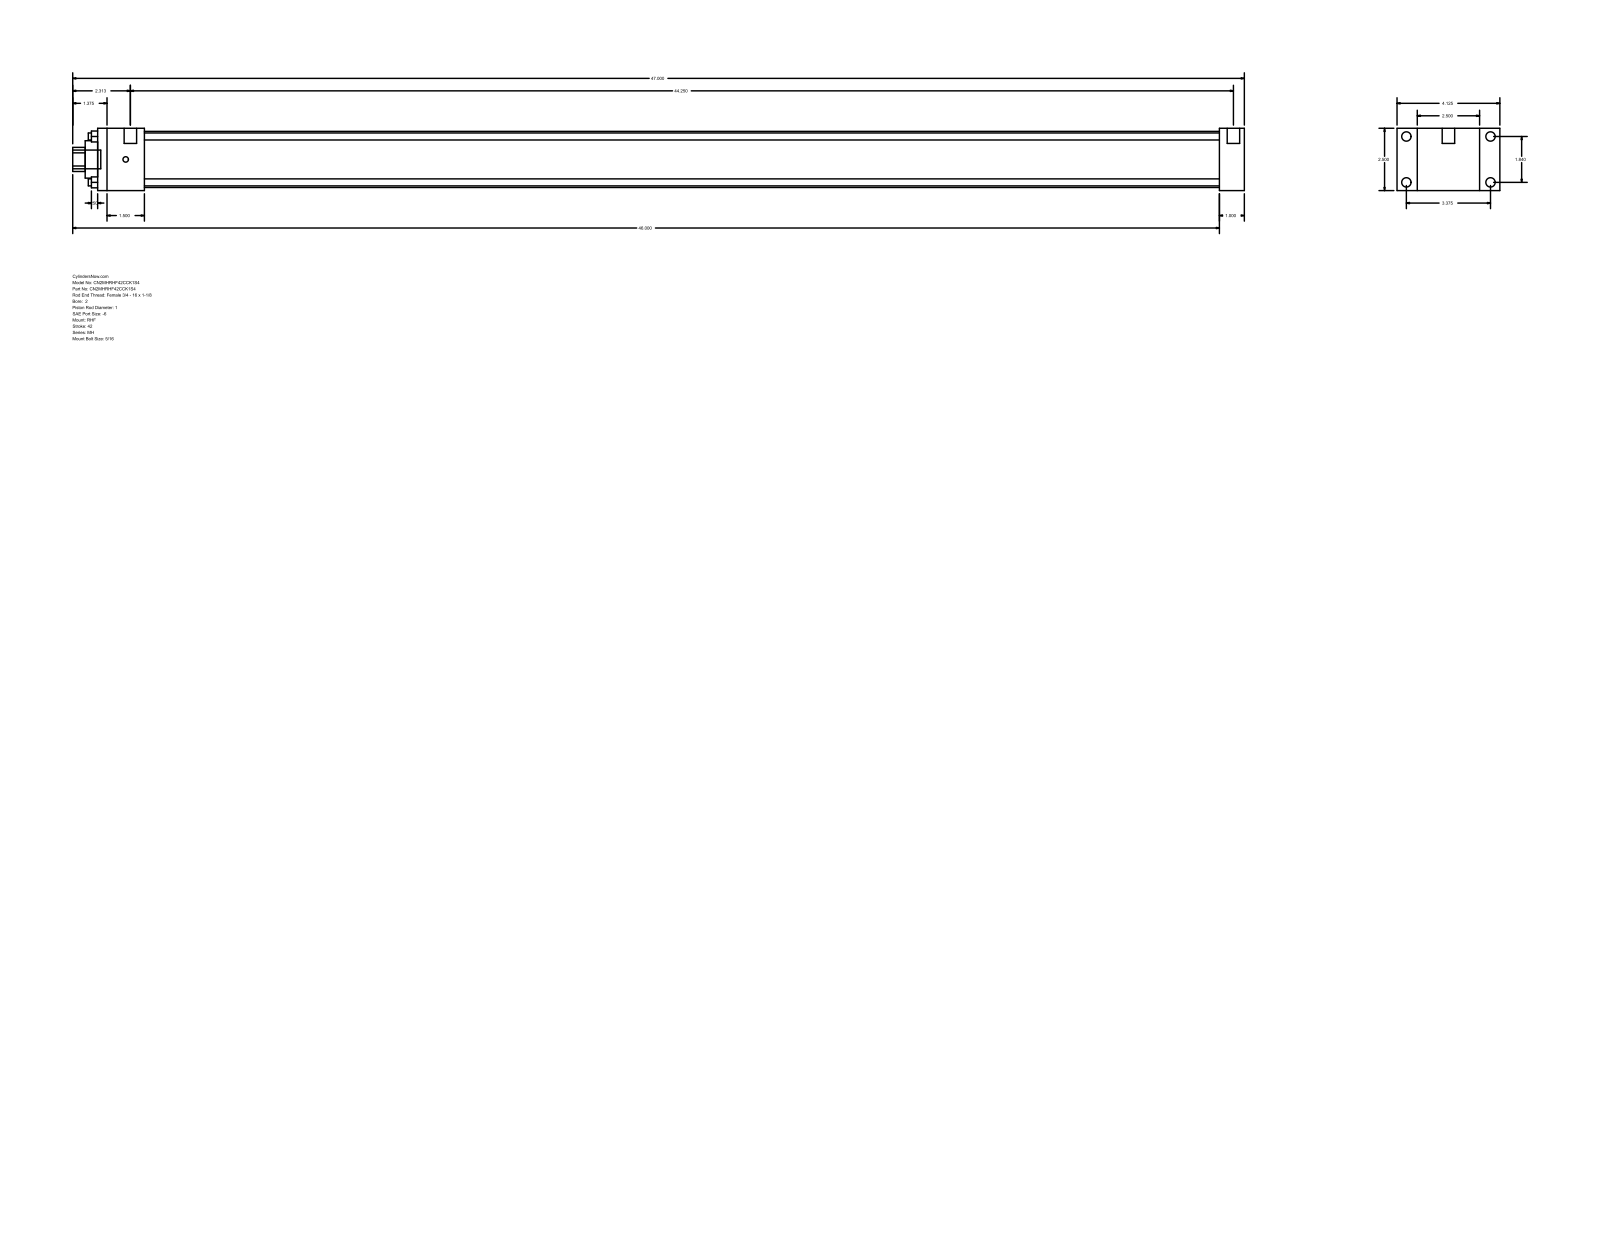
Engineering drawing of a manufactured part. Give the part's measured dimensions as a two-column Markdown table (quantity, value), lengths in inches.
| quantity | value |
| --- | --- |
| part name | MH_RHF__0200_1 |
| STEP written by | GSSL Pune (CONFIG_CONTROL_DESIGN) |
| units | inches |
| bodies | 0 solids, 88 faces (60 planar, 28 cylindrical, 0 other) |
| overall size | 47 × 4.125 × 2.5 |
| round holes (diameter × count) | 0.281 × 4, 1 × 1, 1.5 × 1, 2.25 × 1 |
| round bosses / shafts (diameter × count) | 0.375 × 4, 0.219 × 4, 0.5 × 2, 0.75 × 1 |
| partial cylindrical surfaces (radius × count) | 0.484 × 1 |
| main face-to-face distances | 2.5, 1, 0.813, 3.313, 46, 45, 4.125, 1.875, 43.125, 44.125 |
| hole center spacings | 1.301, 1.84, 2.602 |
